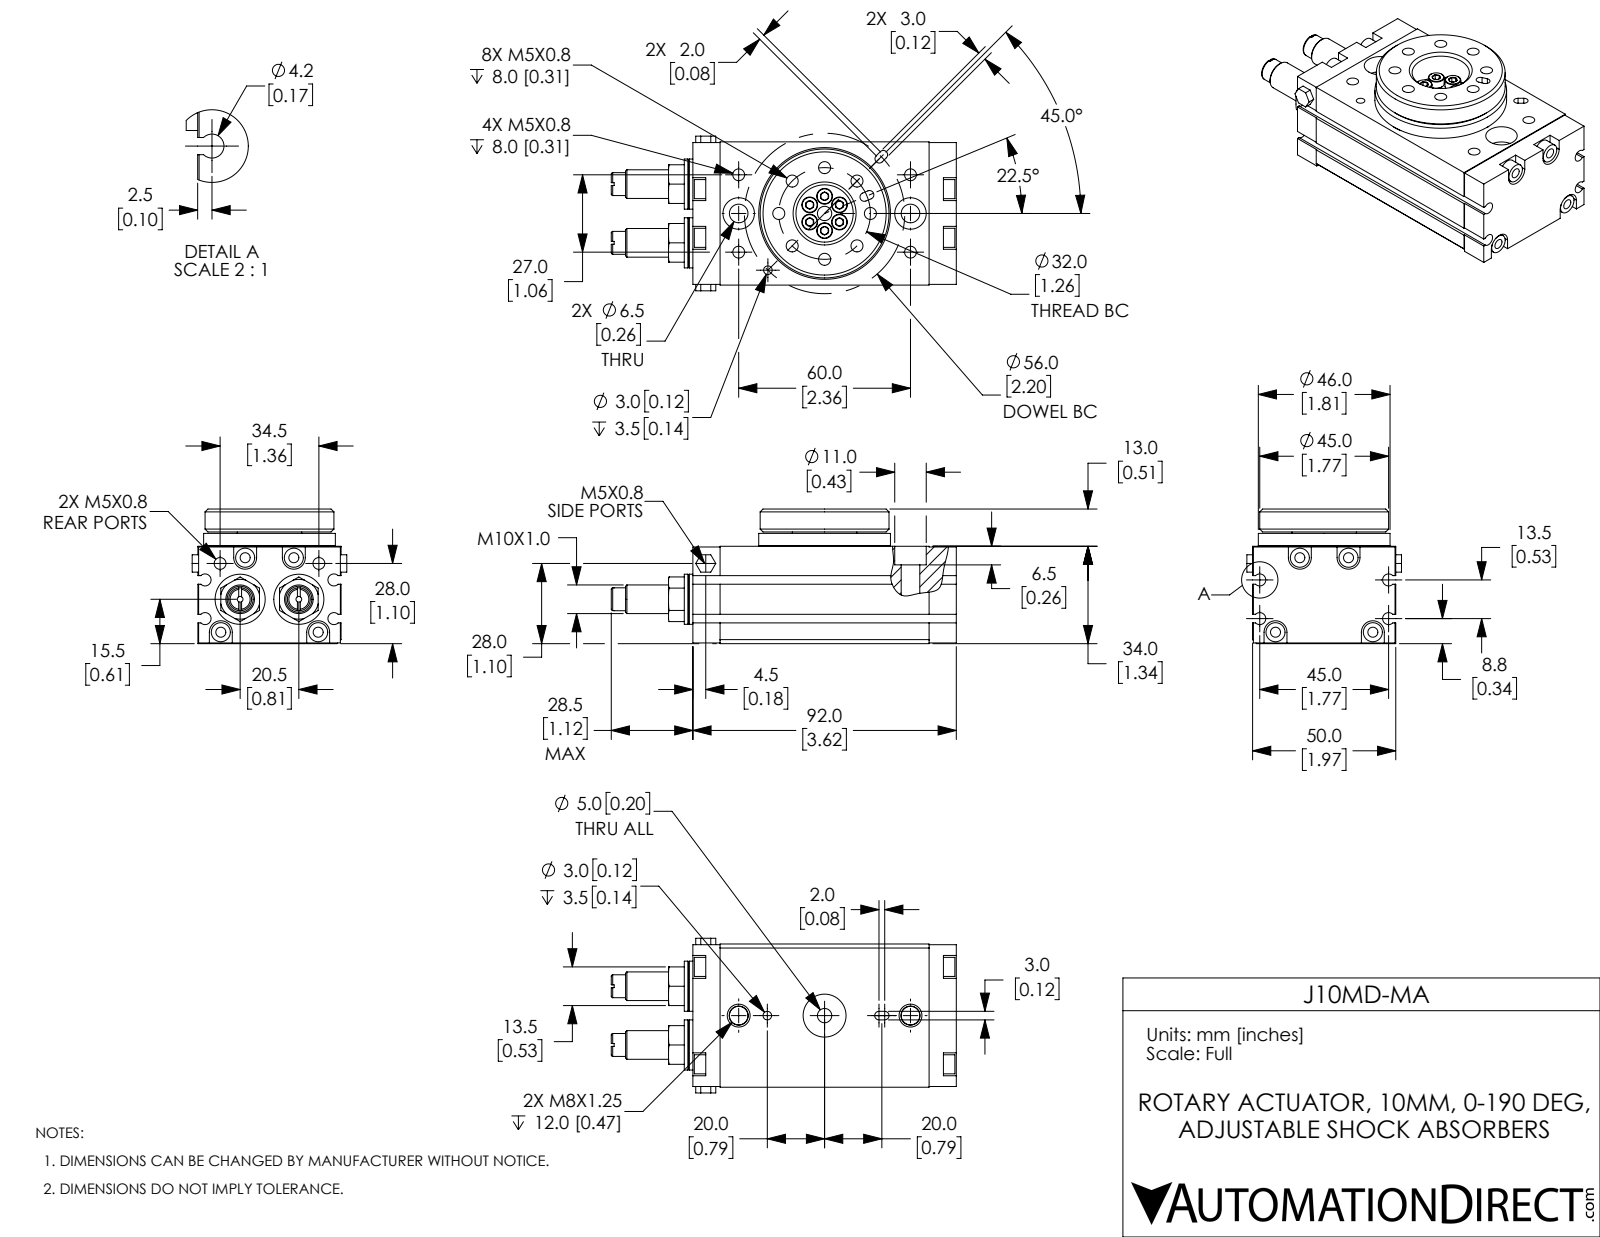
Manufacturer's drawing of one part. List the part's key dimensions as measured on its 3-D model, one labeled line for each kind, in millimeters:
Part name (STEP PRODUCT): J10MD-MA; J10MD-MA_M3_91290A109; J10MD-MA_table; J10MD-MA_BODY
STEP written by: SolidWorks 2017 (AUTOMOTIVE_DESIGN)
Units: millimetres
Bodies: 8 solids, 739 faces (217 planar, 350 cylindrical, 172 other)
Overall size (bounding box): 120.5 × 54 × 47
Volume: 165 250 mm³ · Surface area: 36 778 mm²
Round holes (diameter × count): ⌀4.2 ×8, ⌀4.13 ×6, ⌀3.5 ×4, ⌀2 ×2, ⌀3 ×2, ⌀6.5 ×2, ⌀6.65 ×2, ⌀11 ×2, ⌀5 ×1, ⌀15 ×1, ⌀20 ×1, ⌀23 ×1
Round bosses / shafts (diameter × count): ⌀5.5 ×6, ⌀3 ×6, ⌀2.35 ×6, ⌀6.66 ×4, ⌀17.5 ×2, ⌀10 ×2, ⌀8 ×2, ⌀46 ×1
Partial cylindrical surfaces — rounded edges, fillets, slot ends (radius × count): R1.5 ×6, R2.1 ×4, R4 ×4
Main face-to-face distances: 34, 8, 50, 33.75, 5, 3, 4.5, 13, 38.5, 8.5
Hole centre spacings: 12.24, 29.56, 34, 13.5, 15.99, 16, 18.82, 19.45
